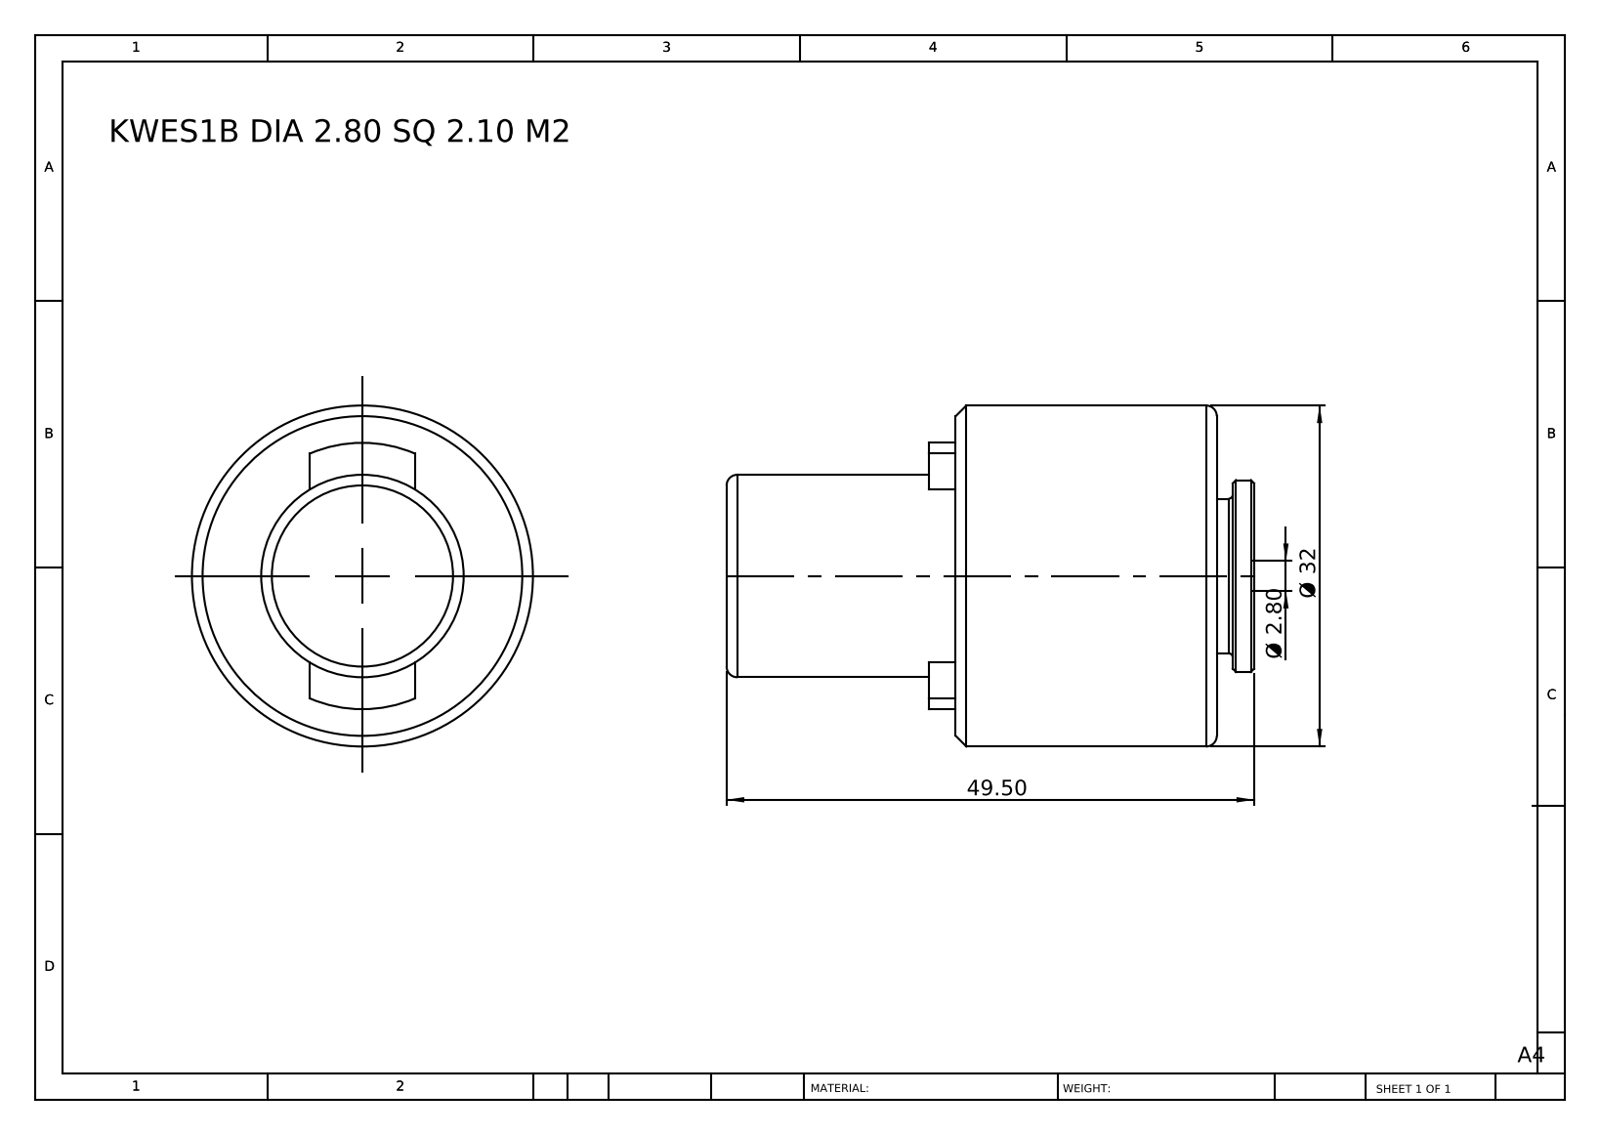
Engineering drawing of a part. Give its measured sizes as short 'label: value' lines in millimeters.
name: KWES1B DIA 2.80 SQ 2.10 3-32'''''''' UNC
written by: SolidWorks 2014 (CONFIG_CONTROL_DESIGN)
unit: mm
bodies: 1 solid, 39 faces (12 planar, 13 cylindrical, 14 other)
size: 49.5 × 32 × 32
volume: 26 537 mm³; area: 5 711 mm²
holes: 1× ⌀2.8
bosses: 1× ⌀32, 1× ⌀19, 1× ⌀18, 1× ⌀14.5
rounds: 1× R12.5
face distances: 24.5, 28, 3.5, 21.5, 46, 49.5, 19, 2.5, 27, 30.5
